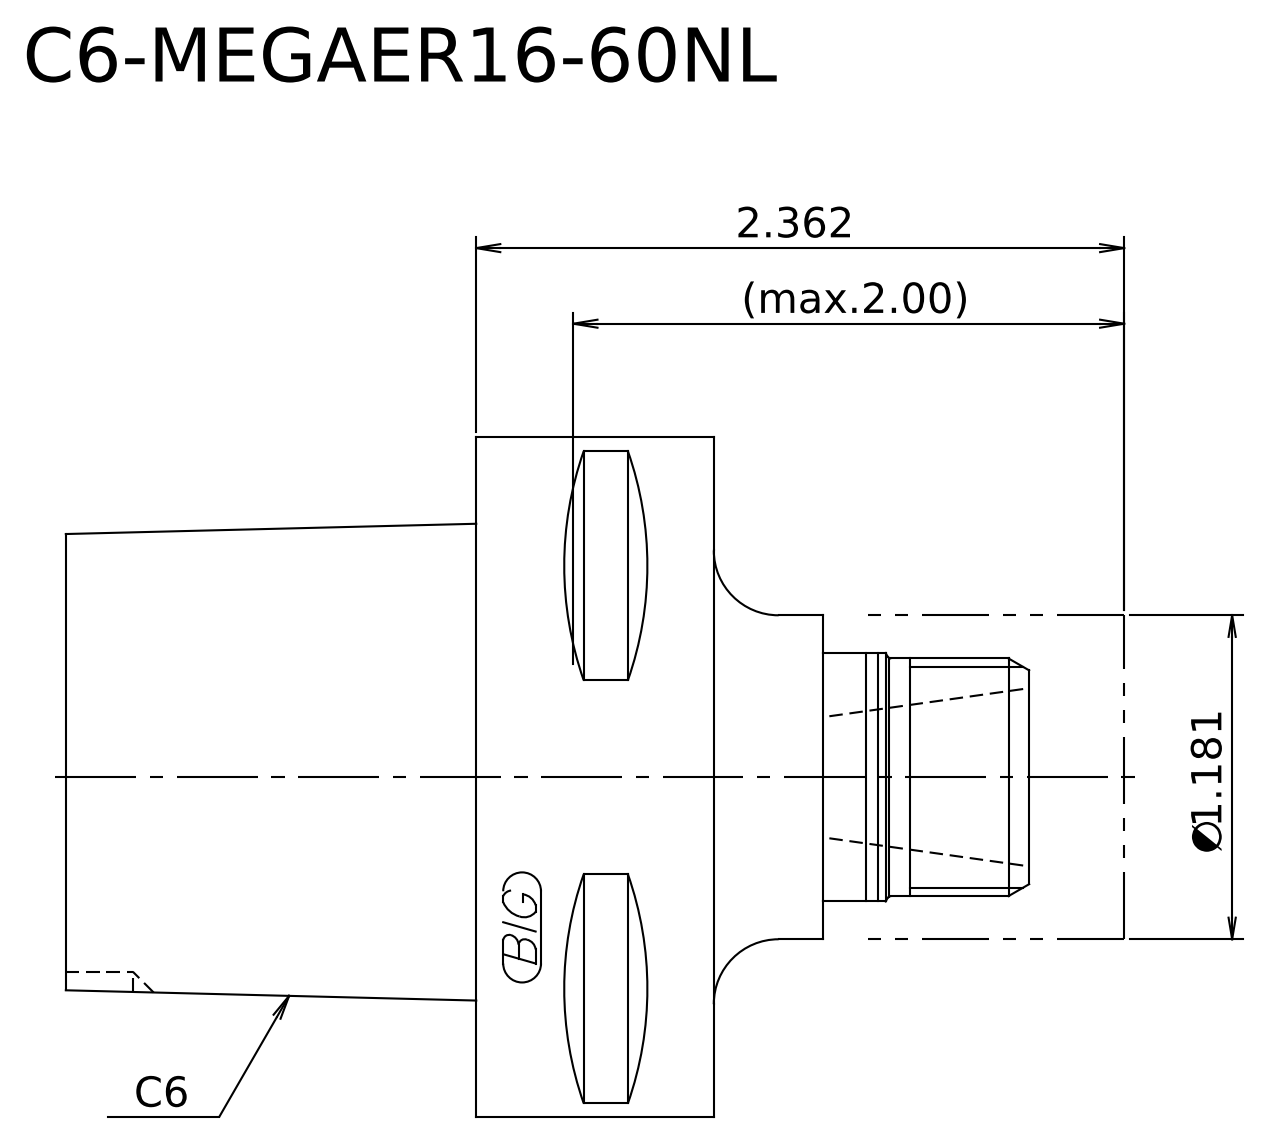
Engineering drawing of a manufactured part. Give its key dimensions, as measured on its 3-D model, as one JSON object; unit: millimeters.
{"step_written_by": "Kubotek KeyCreator 2011 V10.0.2 (22737) (automotive_design)", "units": "millimeters", "bodies": {"solids": 2, "faces": 18, "planar": 7, "cylindrical": 5, "other": 6}, "overall_size": [98, 63, 63], "volume_mm3": 157485, "surface_area_mm2": 21320, "round_bosses_or_shafts": [[63, 1], [30, 1], [23, 1], [22, 1]], "face_to_face_distances": [38, 60, 22, 13, 35, 73, 25, 98, 8.8, 16.2]}
